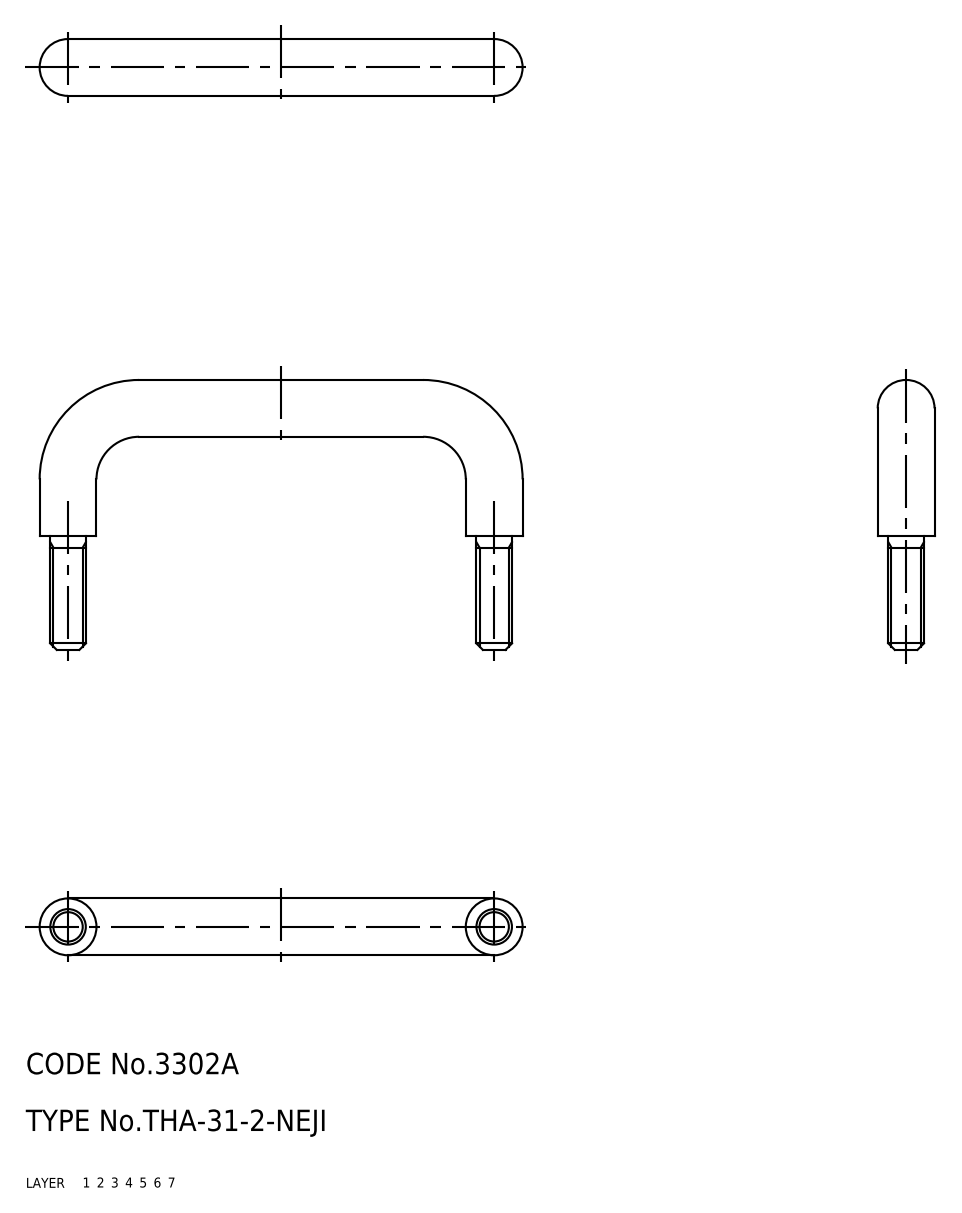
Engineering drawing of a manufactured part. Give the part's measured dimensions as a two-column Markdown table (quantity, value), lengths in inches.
| quantity | value |
| --- | --- |
| part name | pull |
| STEP written by | CADfix (AUTOMOTIVE_DESIGN) |
| units | inches |
| bodies | 1 solid, 22 faces (0 planar, 0 cylindrical, 22 other) |
| overall size | 2.677 × 1.496 × 0.315 |
| volume | 0.306 in³ |
| surface area | 4.314 in² |
